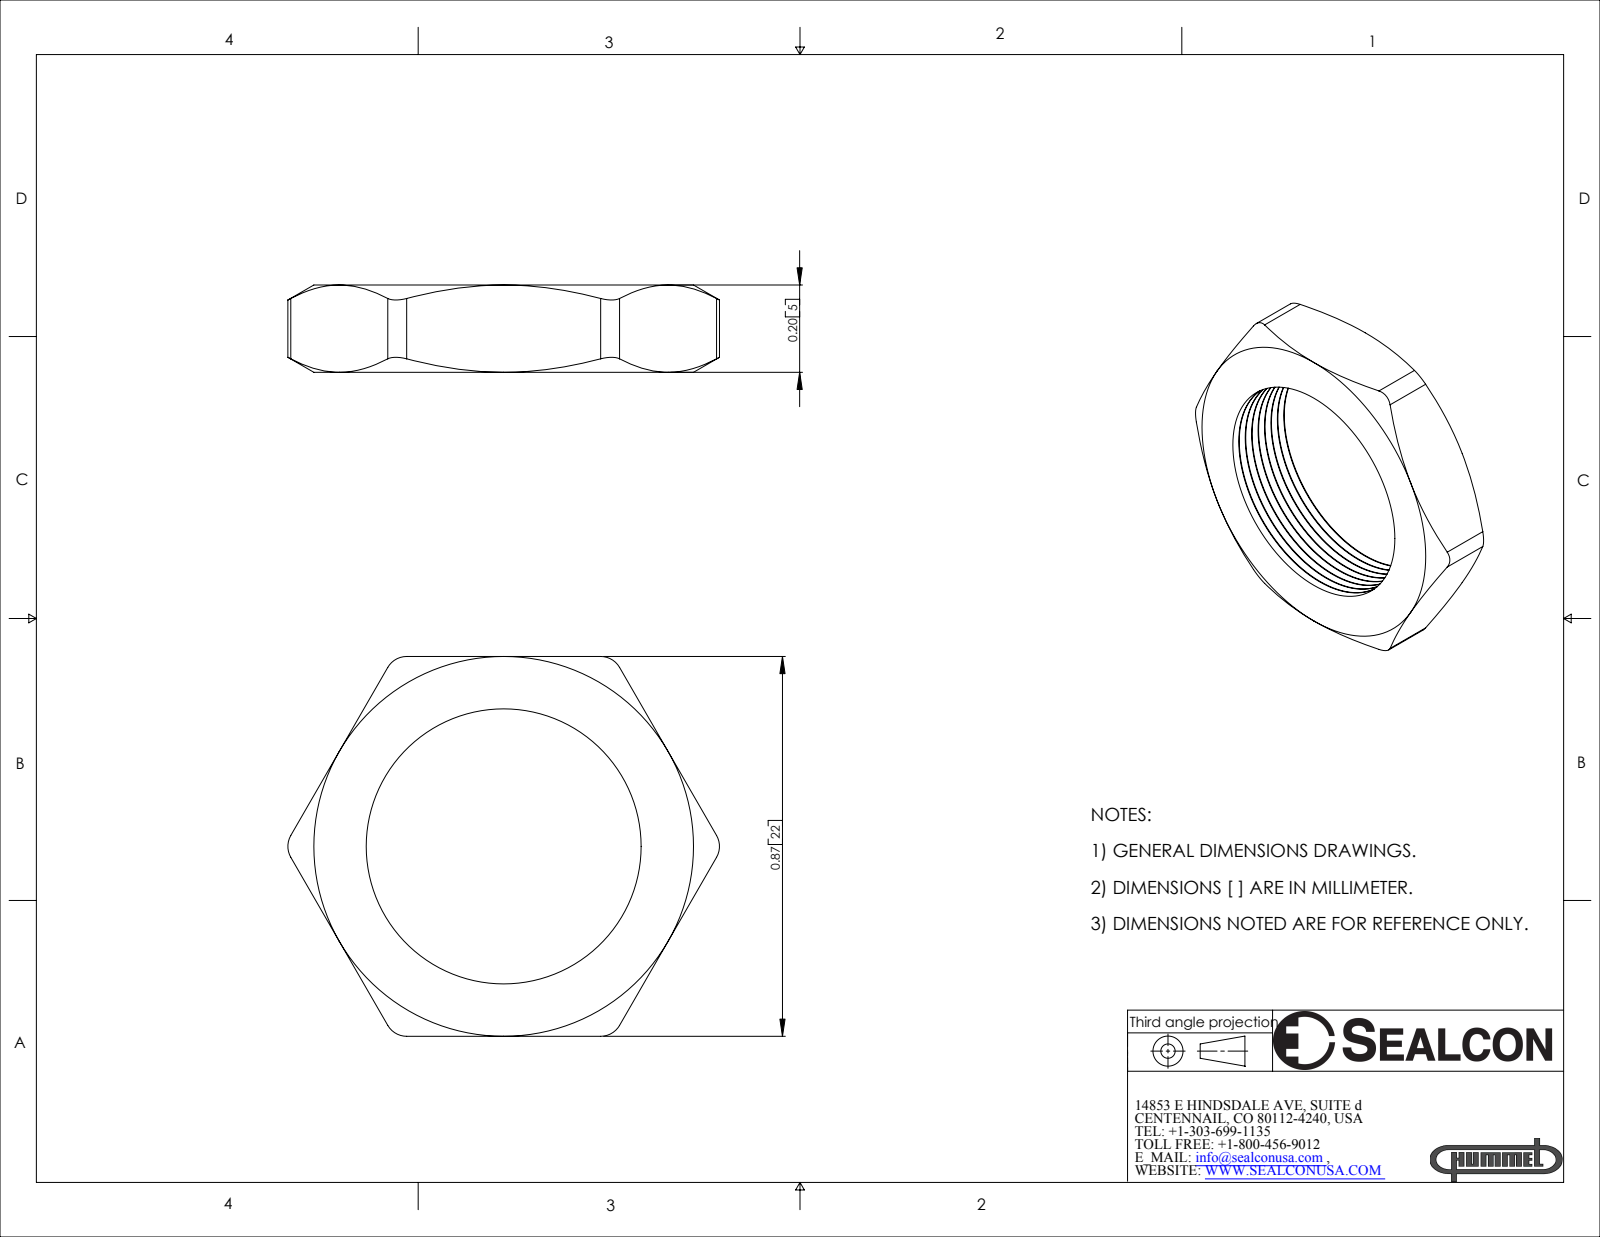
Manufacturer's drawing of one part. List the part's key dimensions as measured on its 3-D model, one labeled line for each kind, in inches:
Part name (STEP PRODUCT): NM-16
STEP written by: SolidWorks 2007 (CONFIG_CONTROL_DESIGN)
Units: inches
Bodies: 1 solid, 77 faces (8 planar, 23 cylindrical, 46 other)
Overall size (bounding box): 0.989 × 0.87 × 0.2
Volume: 0.063 in³ · Surface area: 2.008 in²
Round holes (diameter × count): ⌀0.63 ×1
Partial cylindrical surfaces — rounded edges, fillets, slot ends (radius × count): R0.05 ×6
Main face-to-face distances: 0.2, 0.87
